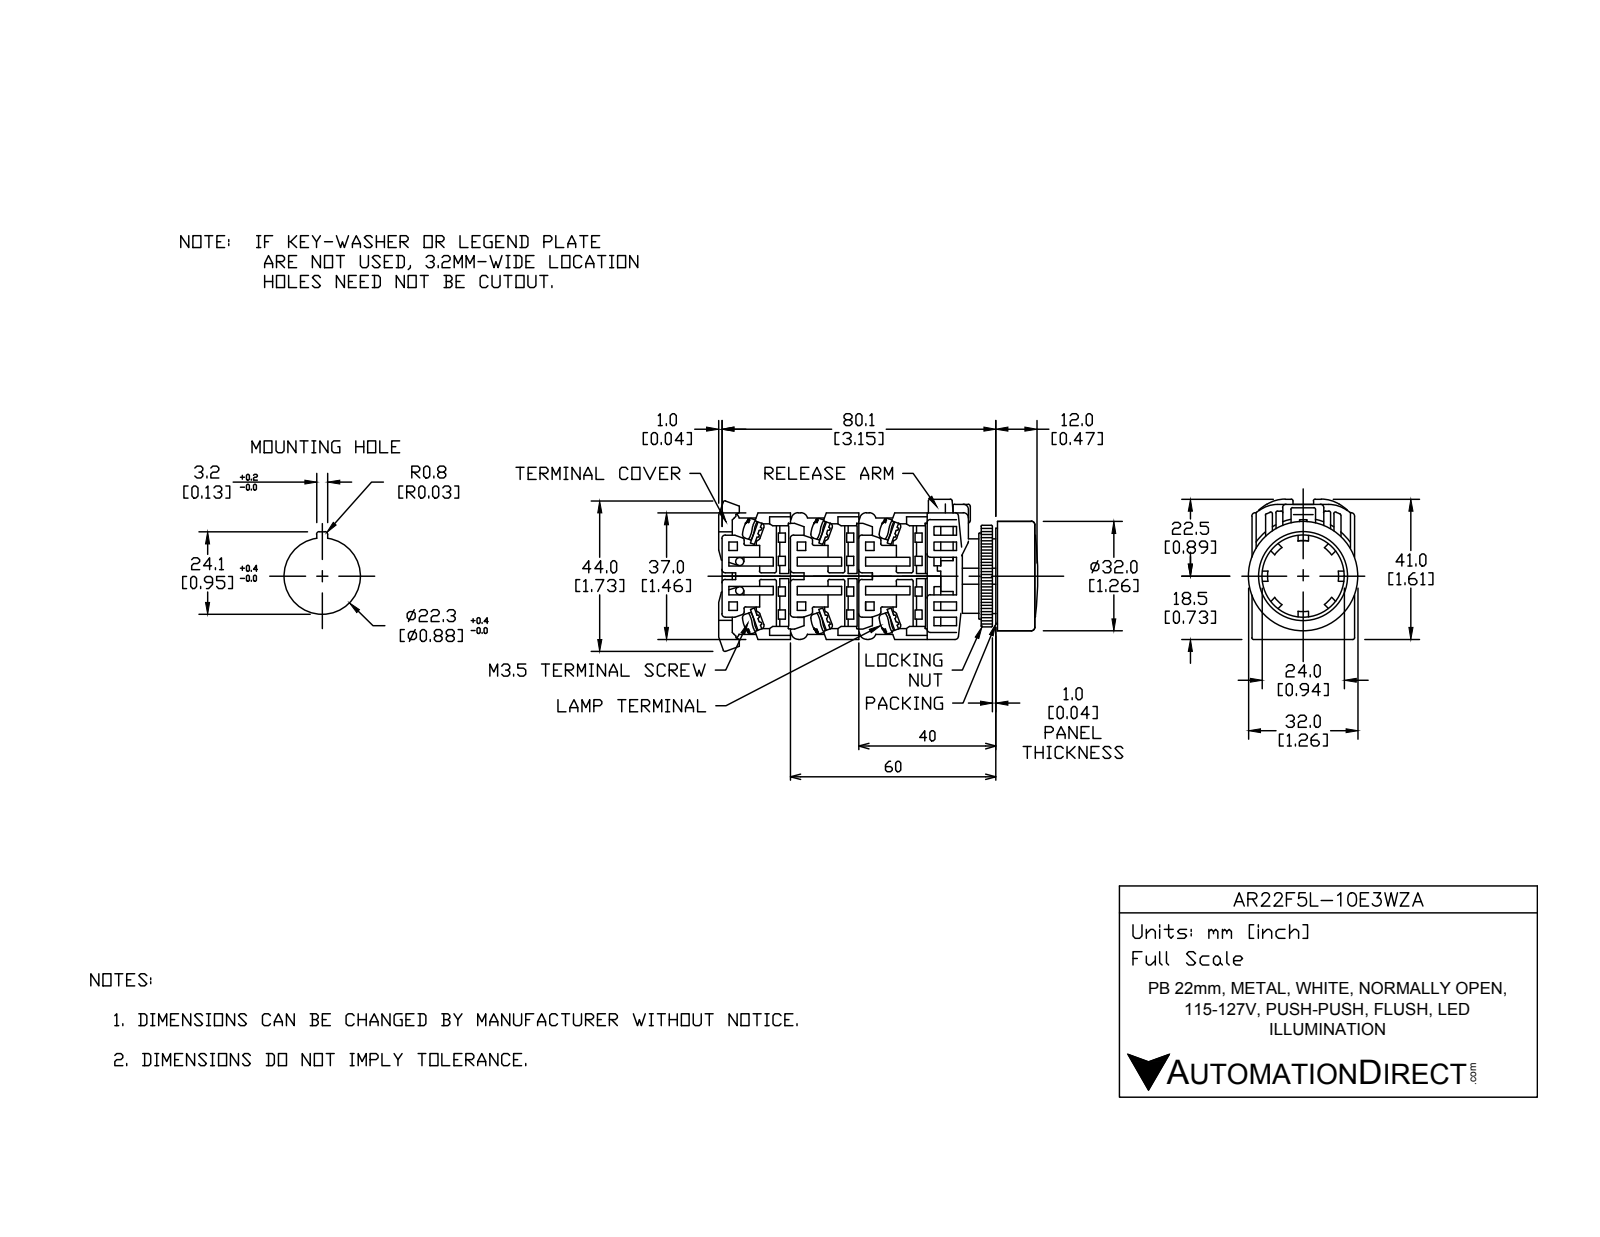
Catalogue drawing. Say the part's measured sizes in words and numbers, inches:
The part is named "AR22F5L-10E3WZA". Its 3-D file was written by "SolidWorks 2017 (AUTOMOTIVE_DESIGN)". It is 18 solids with 475 faces: 329 planar, 111 cylindrical and 35 other. Overall it measures 2.077 by 1.725 by 1.26 inches. Its volume is 2.219 cubic inches and its surface area 37.3 square inches. Round holes: 1 of diameter 0.858, 1 of diameter 0.866, 1 of diameter 0.984, 1 of diameter 1.22. Round bosses or shafts: 4 of diameter 0.197, 1 of diameter 1.26, 1 of diameter 1.201, 1 of diameter 1.173, 1 of diameter 0.945, 1 of diameter 0.937, 1 of diameter 0.856, 1 of diameter 0.669. Partial cylindrical surfaces (rounded edges, fillets, slot ends): 39 of radius 0.02, 8 of radius 0.069, 4 of radius 0.197, 2 of radius 0.157, 1 of radius 0.653, 1 of radius 0.693. The main face-to-face distances are 0.039, 0.709, 1.122, 1.909, 0.787, 1.142, 0.118, 0.079, 0.827, 0.02.
